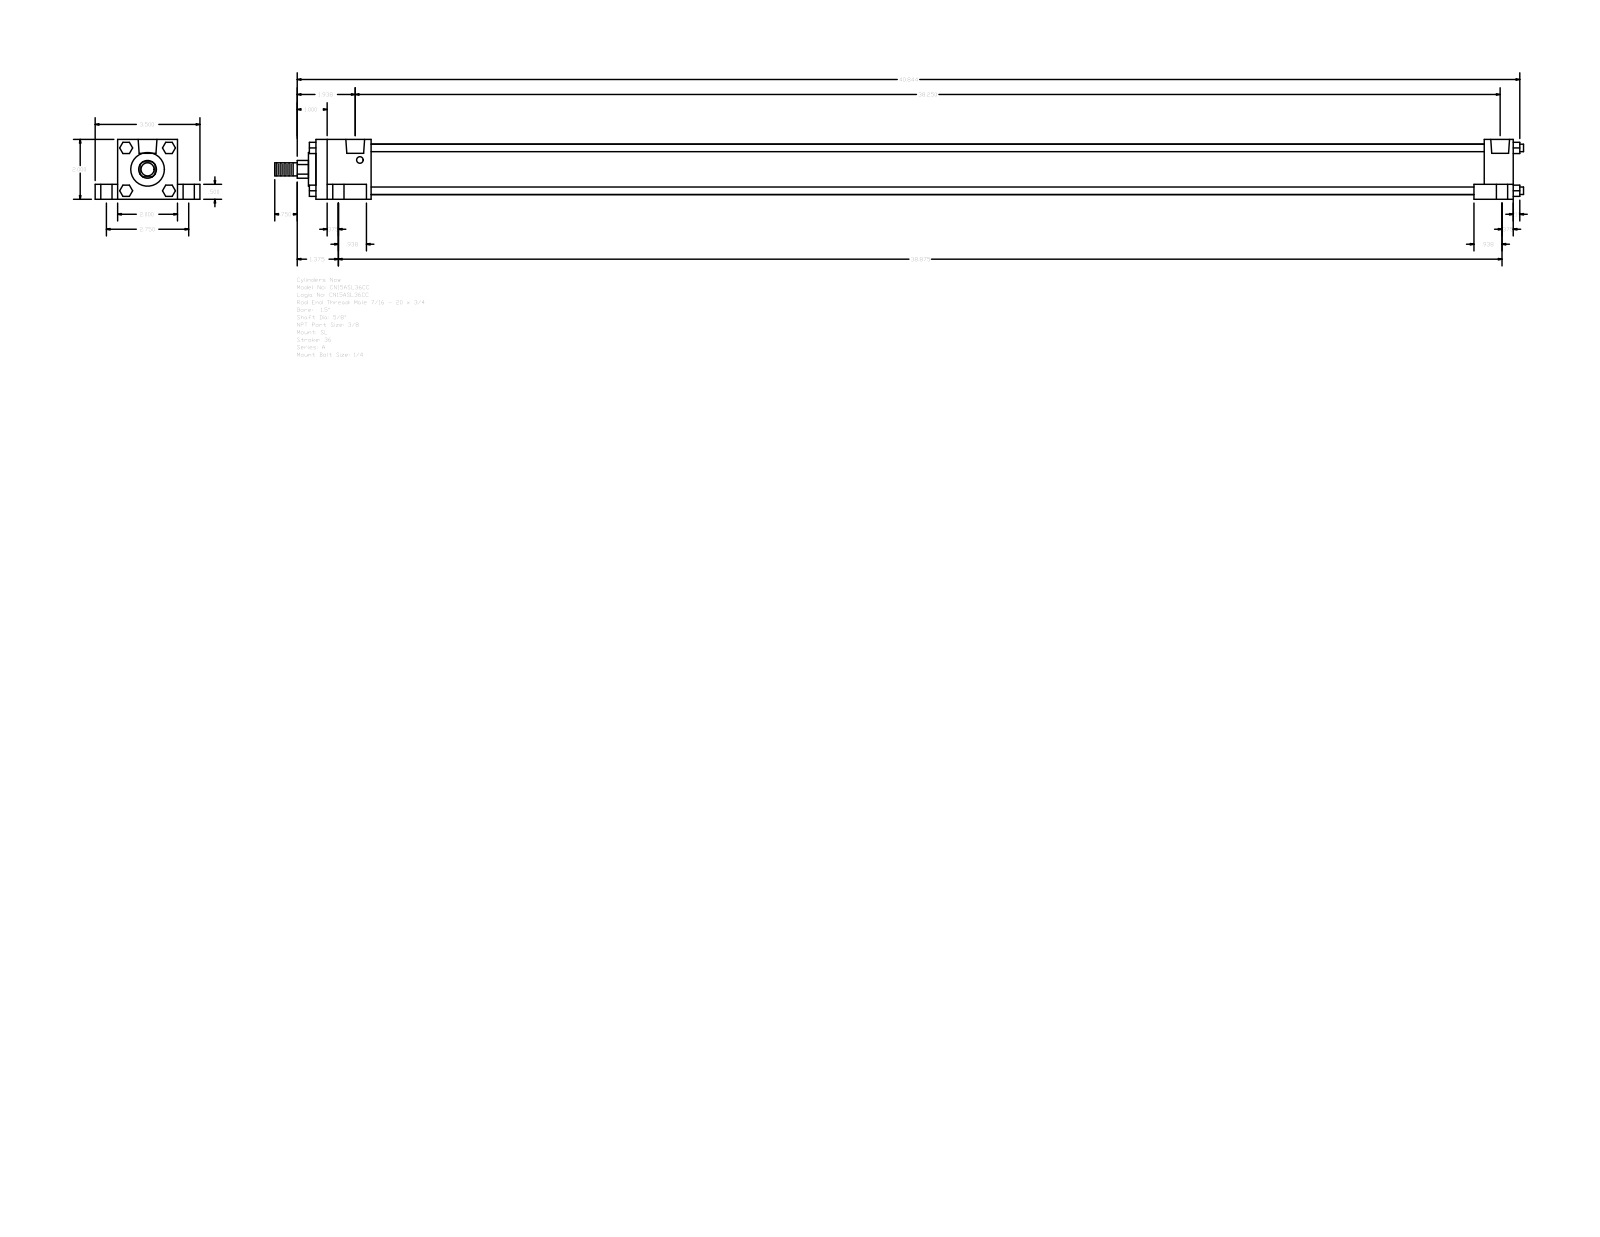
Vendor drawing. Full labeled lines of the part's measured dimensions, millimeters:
Part name (STEP PRODUCT): A_SL__0150_0.625
STEP written by: GSSL Pune (CONFIG_CONTROL_DESIGN)
Units: millimetres
Bodies: 0 solids, 148 faces (112 planar, 36 cylindrical, 0 other)
Overall size (bounding box): 1059.66 × 88.9 × 50.8
Round holes (diameter × count): ⌀5.56 ×4, ⌀9.53 ×4, ⌀15.88 ×4, ⌀15.93 ×2
Round bosses / shafts (diameter × count): ⌀6.35 ×4, ⌀42.93 ×1, ⌀28.57 ×1, ⌀15.88 ×1, ⌀11.11 ×1
Partial cylindrical surfaces — rounded edges, fillets, slot ends (radius × count): R7.54 ×1
Main face-to-face distances: 50.8, 19.05, 38.1, 12.7, 69.85, 1016, 9.52, 33.34, 991.39, 24.61
Hole centre spacings: 3.97, 34.96, 35.36, 37.73, 39.41, 69.84, 963.61, 967.58
